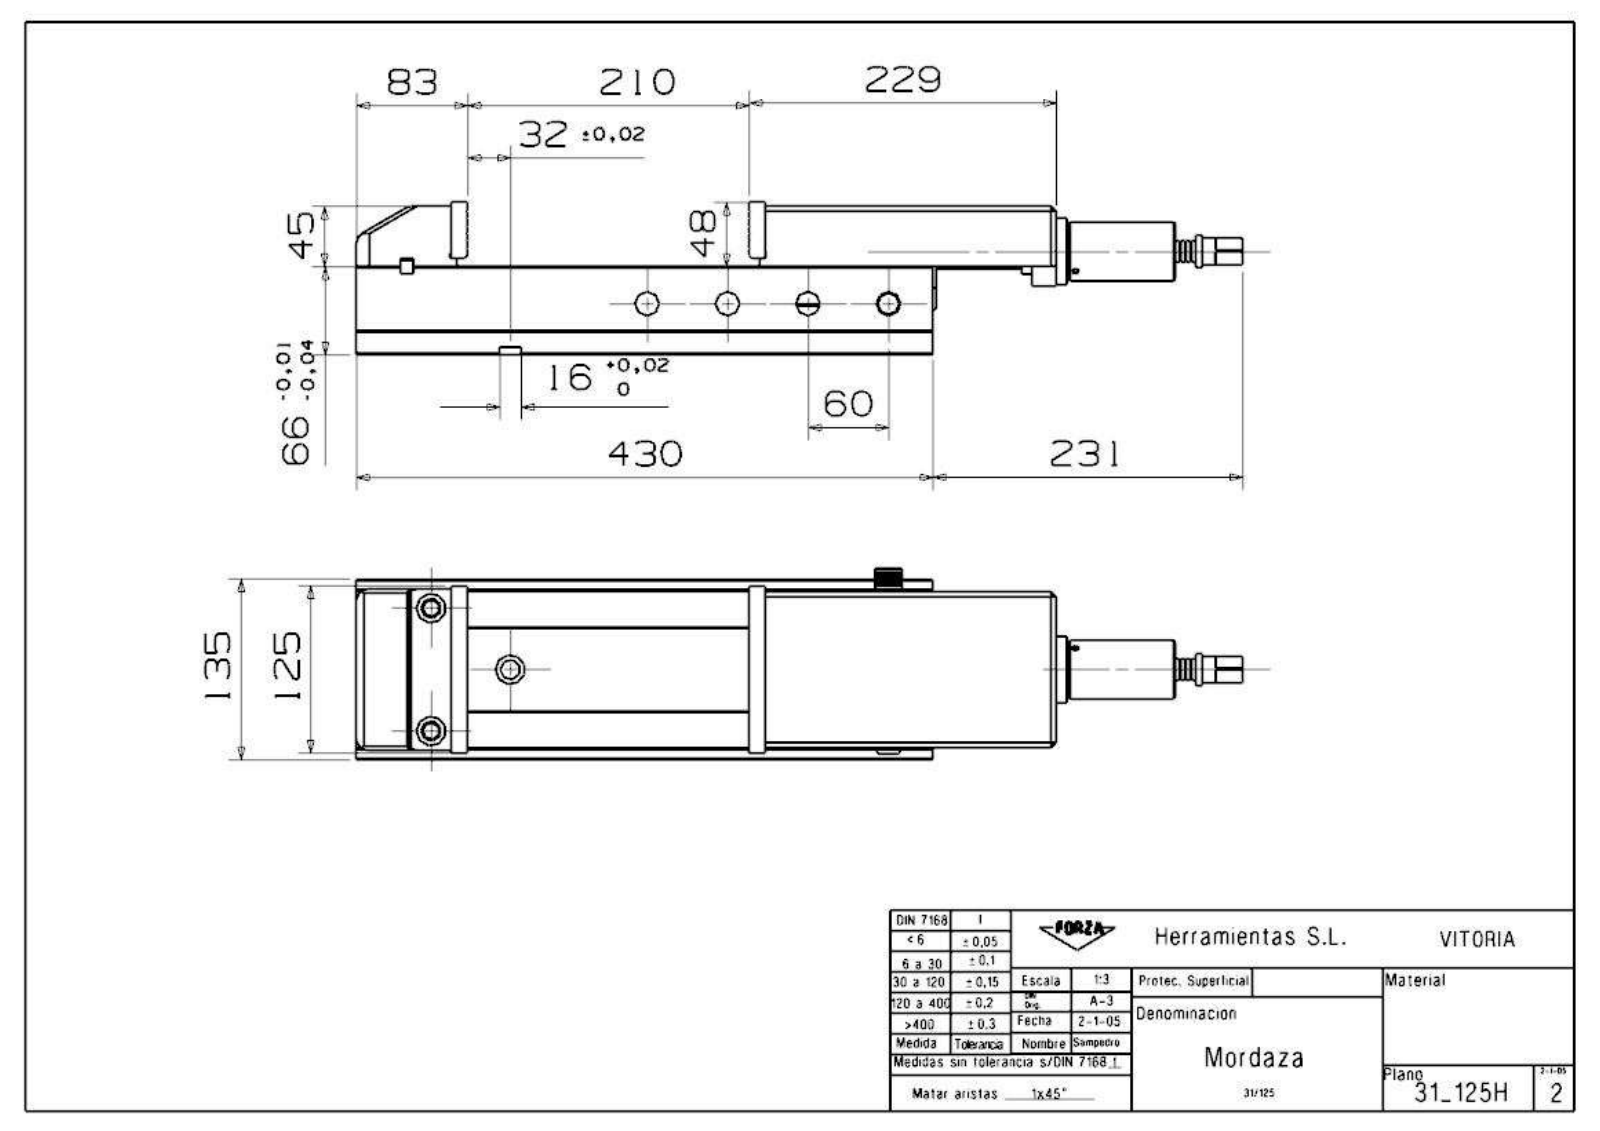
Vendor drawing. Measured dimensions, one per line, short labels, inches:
name: 31_125H_Mordaza
written by: SIEMENS PLM Software NX 7.5 (AUTOMOTIVE_DESIGN)
unit: in
bodies: 24 solids, 650 faces (394 planar, 161 cylindrical, 95 other)
size: 26.024 × 5.65 × 4.488
volume: 237.9 in³; area: 927 in²
holes: 6× ⌀0.204, 6× ⌀0.591, 6× ⌀0.866, 5× ⌀0.394, 5× ⌀0.709, 4× ⌀0.197, 4× ⌀0.275, 4× ⌀0.487, 4× ⌀0.551, 2× ⌀0.135, 2× ⌀0.157, 2× ⌀0.171
bosses: 2× ⌀0.787, 1× ⌀1.969, 1× ⌀1.732, 1× ⌀1.535, 1× ⌀1.496, 1× ⌀1.378, 1× ⌀1.26, 1× ⌀1.22
rounds: 6× R0.118, 2× R0.031, 2× R0.315, 2× R0.394, 1× R0.079, 1× R0.47, 1× R0.472, 1× R0.984
face distances: 2.598, 1.012, 1.587, 0.866, 4.37, 3.358, 1.772, 0.059, 3.799, 3.858
hole spacings: 1.083, 2.362, 0.551, 0.63, 0.641, 0.645, 0.702, 0.837
